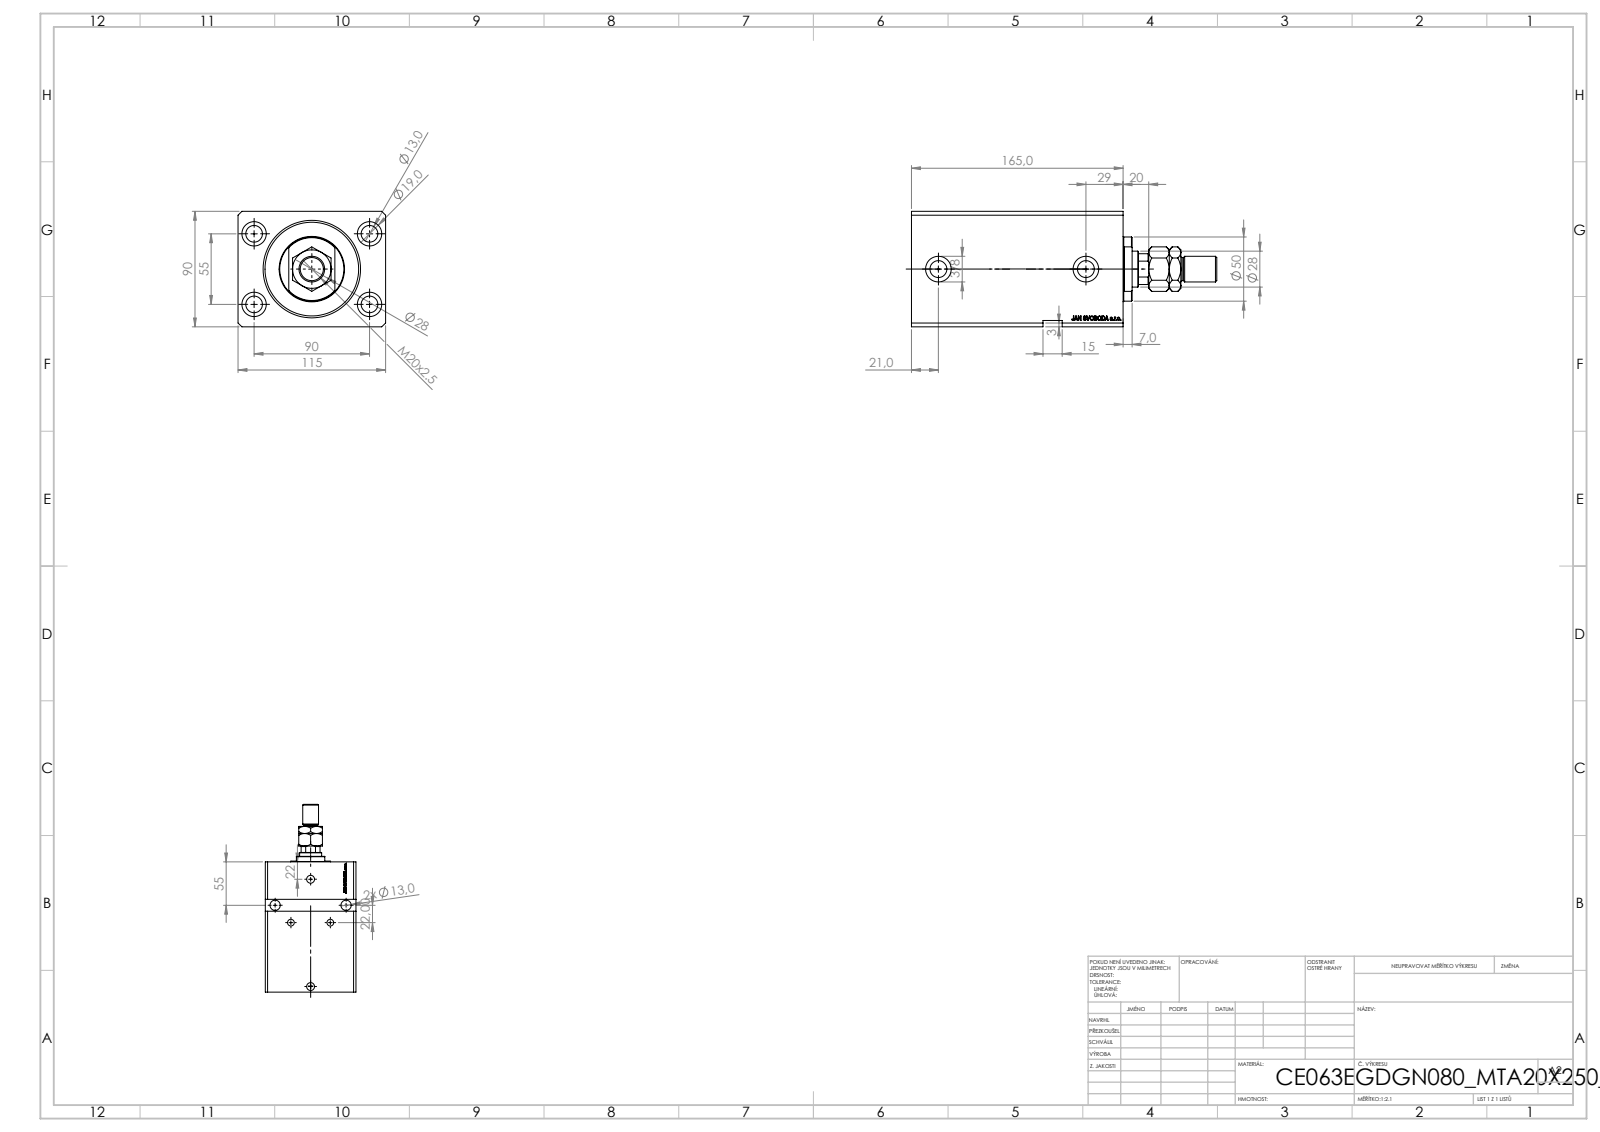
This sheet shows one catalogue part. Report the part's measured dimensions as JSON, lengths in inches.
{"part_name": "V250CE_E_Body; V250CE_C_VCP; MTA; V250CE_VC_E", "step_written_by": "SolidWorks 2019 (CONFIG_CONTROL_DESIGN)", "units": "inches", "bodies": {"solids": 4, "faces": 1010, "planar": 486, "cylindrical": 108, "other": 416}, "overall_size": [9.37, 4.528, 3.543], "volume_in3": 85.37, "surface_area_in2": 317.1, "round_holes": [[0.512, 6], [0.049, 4], [0.748, 4], [0.335, 2], [0.394, 2], [0.518, 2], [0.787, 2], [0.728, 1], [1.102, 1], [2.48, 1], [2.992, 1]], "round_bosses_or_shafts": [[1.969, 1], [0.787, 1], [0.709, 1]], "partial_cylinders_radius": [[0.531, 1]], "face_to_face_distances": [3.543, 4.528, 0.787, 6.496, 0.705, 5.791, 5.709, 5.004, 2.559, 0.512], "hole_center_spacings": [2.076, 3.543, 1.17, 2.165, 2.197, 2.379, 2.889, 3.317]}
